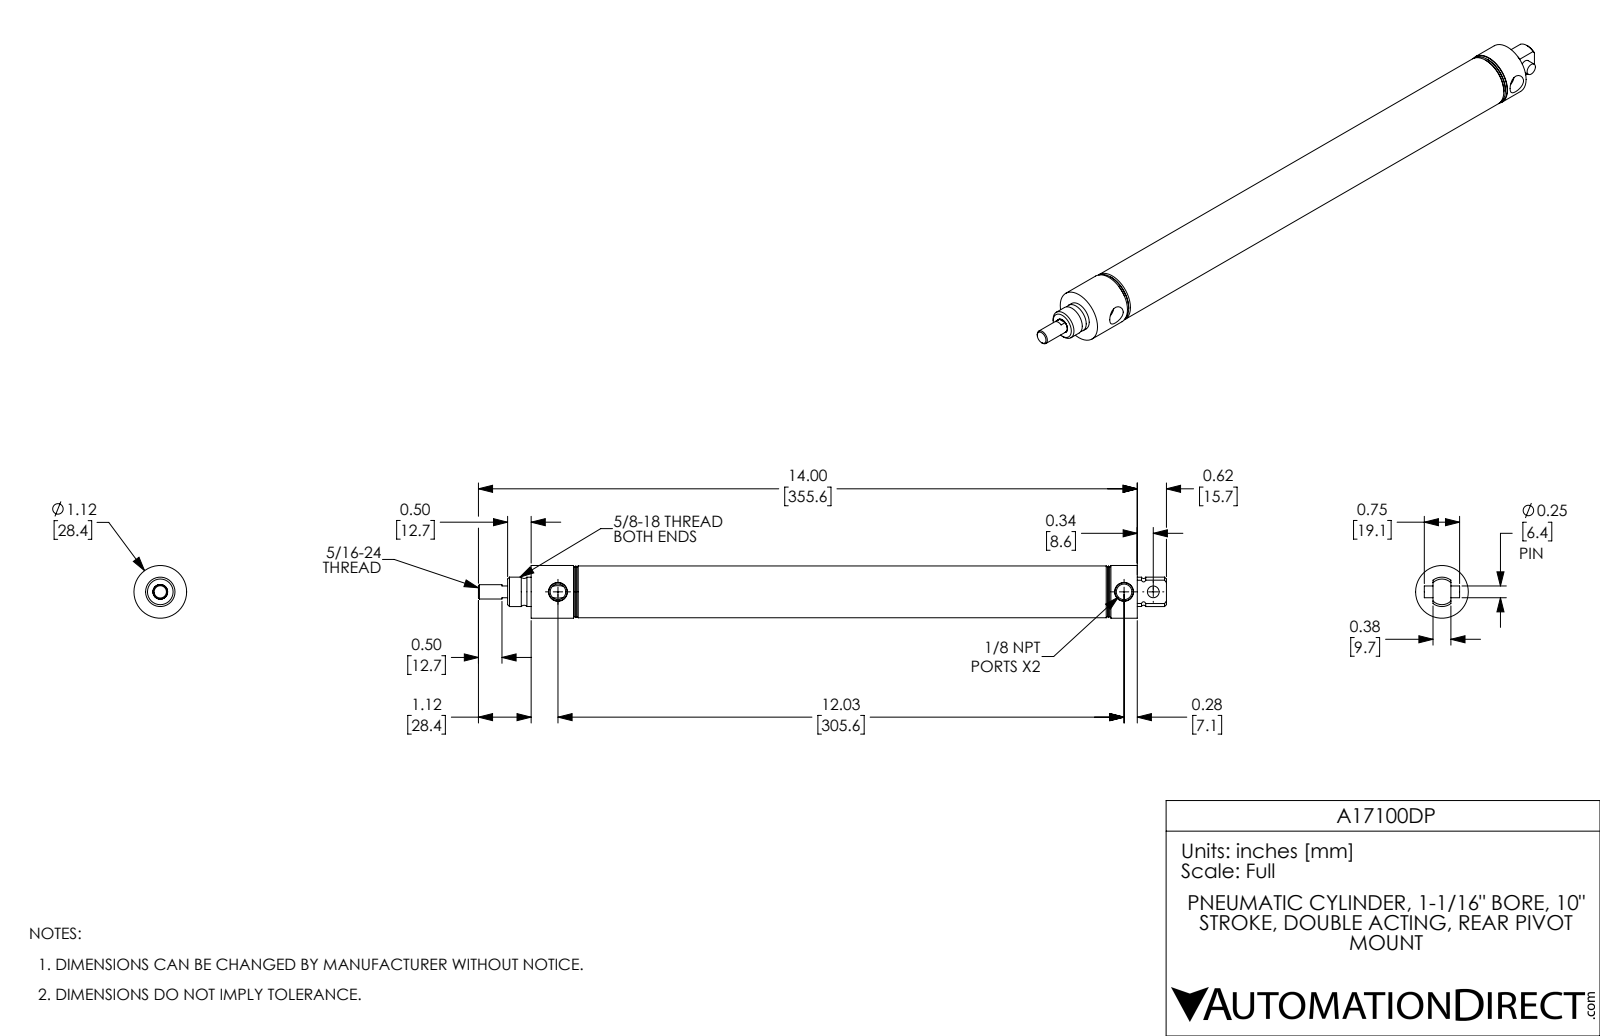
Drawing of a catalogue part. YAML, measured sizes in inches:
part_name: "A17100DP; A17100DP-PIN; A17100DP-Rod; A17100DP-MainBody"
step_written_by: "SolidWorks 2017 (AUTOMOTIVE_DESIGN)"
units: inches
bodies: {solids: 3, faces: 92, planar: 22, cylindrical: 32, other: 38}
overall_size: [14.62, 1.12, 1.12]
volume: 4.427
surface_area: 104.5
round_holes:
  - {diameter: 0.332, count: 2}
  - {diameter: 0.25, count: 1}
  - {diameter: 0.312, count: 1}
  - {diameter: 1.063, count: 1}
round_bosses_or_shafts:
  - {diameter: 1.12, count: 1}
  - {diameter: 1.1, count: 1}
  - {diameter: 0.625, count: 1}
  - {diameter: 0.623, count: 1}
  - {diameter: 0.304, count: 1}
partial_cylinders:
  - {radius: 0.313, count: 1}
face_to_face_distances: [0.5, 11.69, 10.5, 10, 1.19, 1.69, 11.69, 12.88, 11.19, 1.19]
hole_center_spacings: [0.62, 12.03, 12.65]
